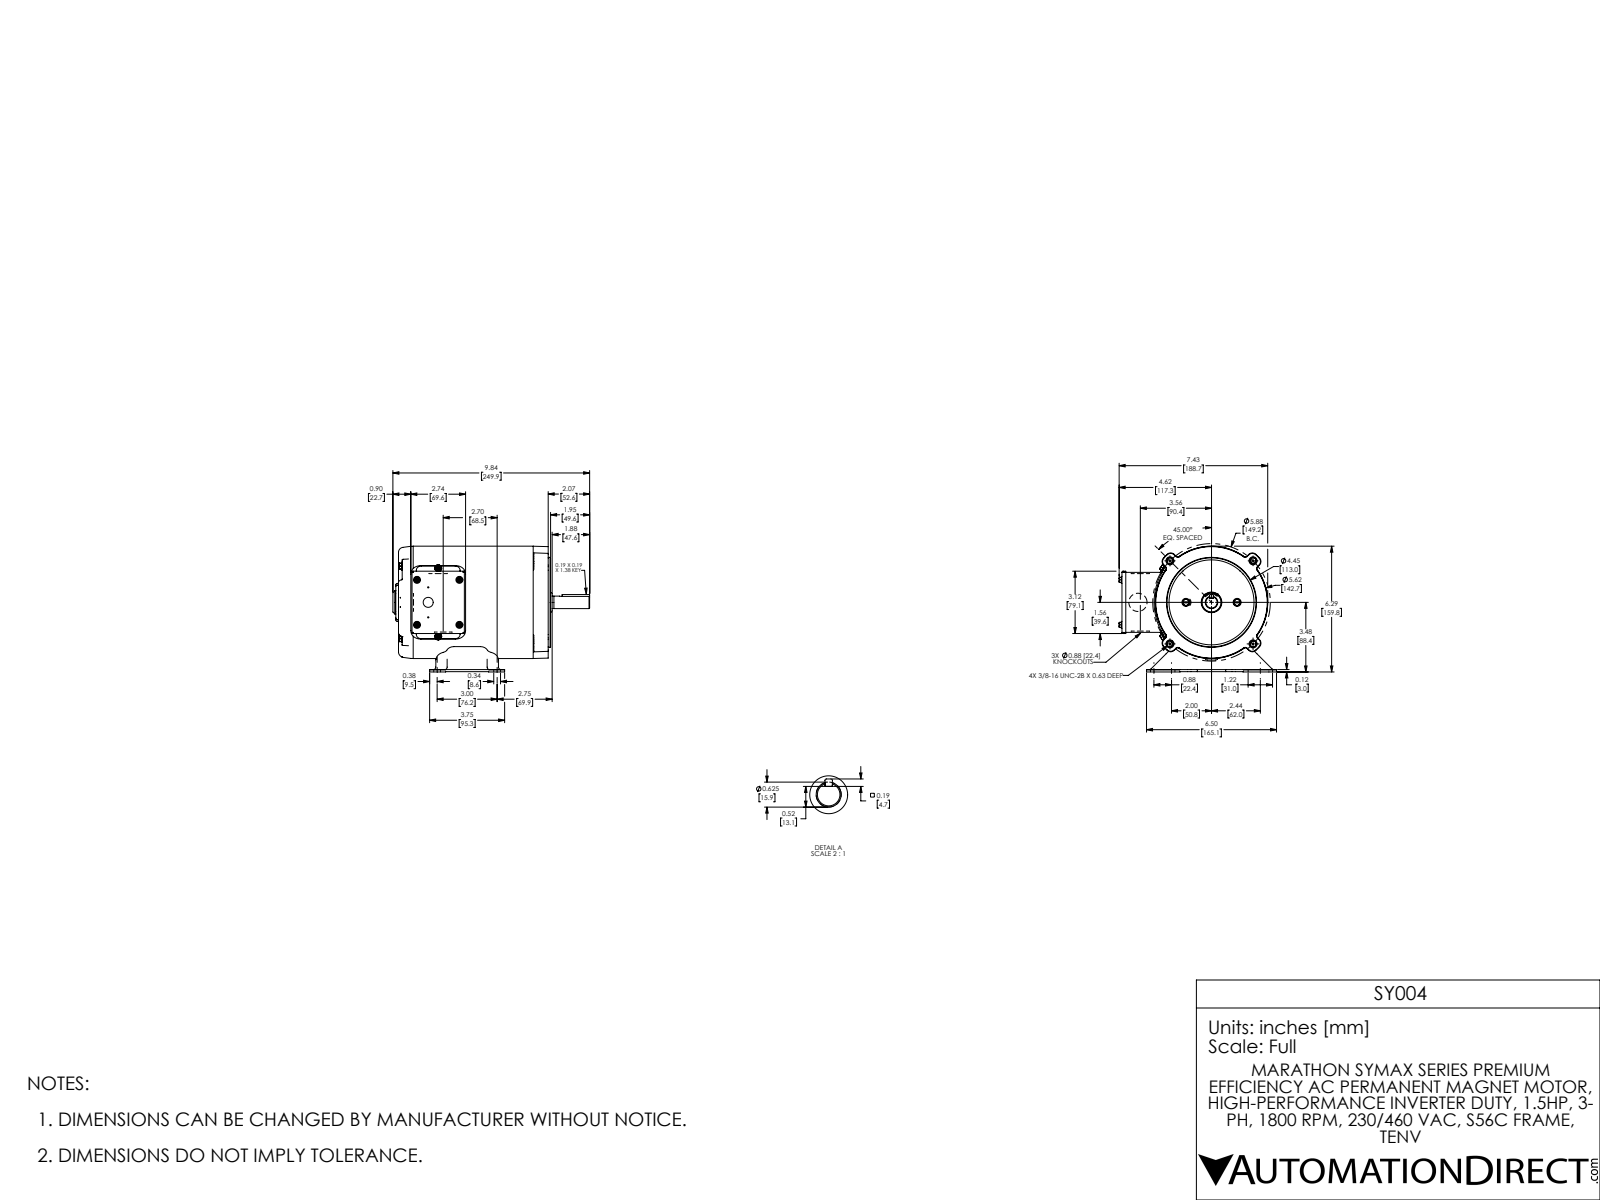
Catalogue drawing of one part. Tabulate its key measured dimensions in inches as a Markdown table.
| quantity | value |
| --- | --- |
| part name | 614-0004-004_RevE_56TC_1P5HP Coord |
| STEP written by | SolidWorks 2017 (AUTOMOTIVE_DESIGN) |
| units | inches |
| bodies | 25 solids, 4745 faces (2373 planar, 581 cylindrical, 1791 other) |
| overall size | 9.837 × 7.869 × 6.29 |
| volume | 32.36 in³ |
| surface area | 618.1 in² |
| round holes (diameter × count) | 0.22 × 6, 0.19 × 5, 0.06 × 4, 0.136 × 4, 0.201 × 4, 0.25 × 4, 0.88 × 3, 0.154 × 2, 0.226 × 2, 0.28 × 2, 0.5 × 1, 0.67 × 1 |
| round bosses / shafts (diameter × count) | 0.399 × 6, 0.348 × 6, 0.19 × 6, 0.164 × 6, 0.166 × 4, 0.91 × 3, 5.62 × 1, 5.497 × 1 |
| partial cylindrical surfaces (radius × count) | 0.06 × 54, 0.045 × 40, 0.03 × 32, 0.13 × 22, 0.17 × 18, 0.25 × 14, 0.16 × 12, 0.38 × 12 |
| main face-to-face distances | 0.048, 0.09, 7.485, 7.395, 0.104, 2.452, 0.015, 2.952, 6.75, 0.13 |
| hole center spacings | 2.12, 3.091, 1.893, 2.25, 2.562, 3.624, 4.548, 0.75 |
